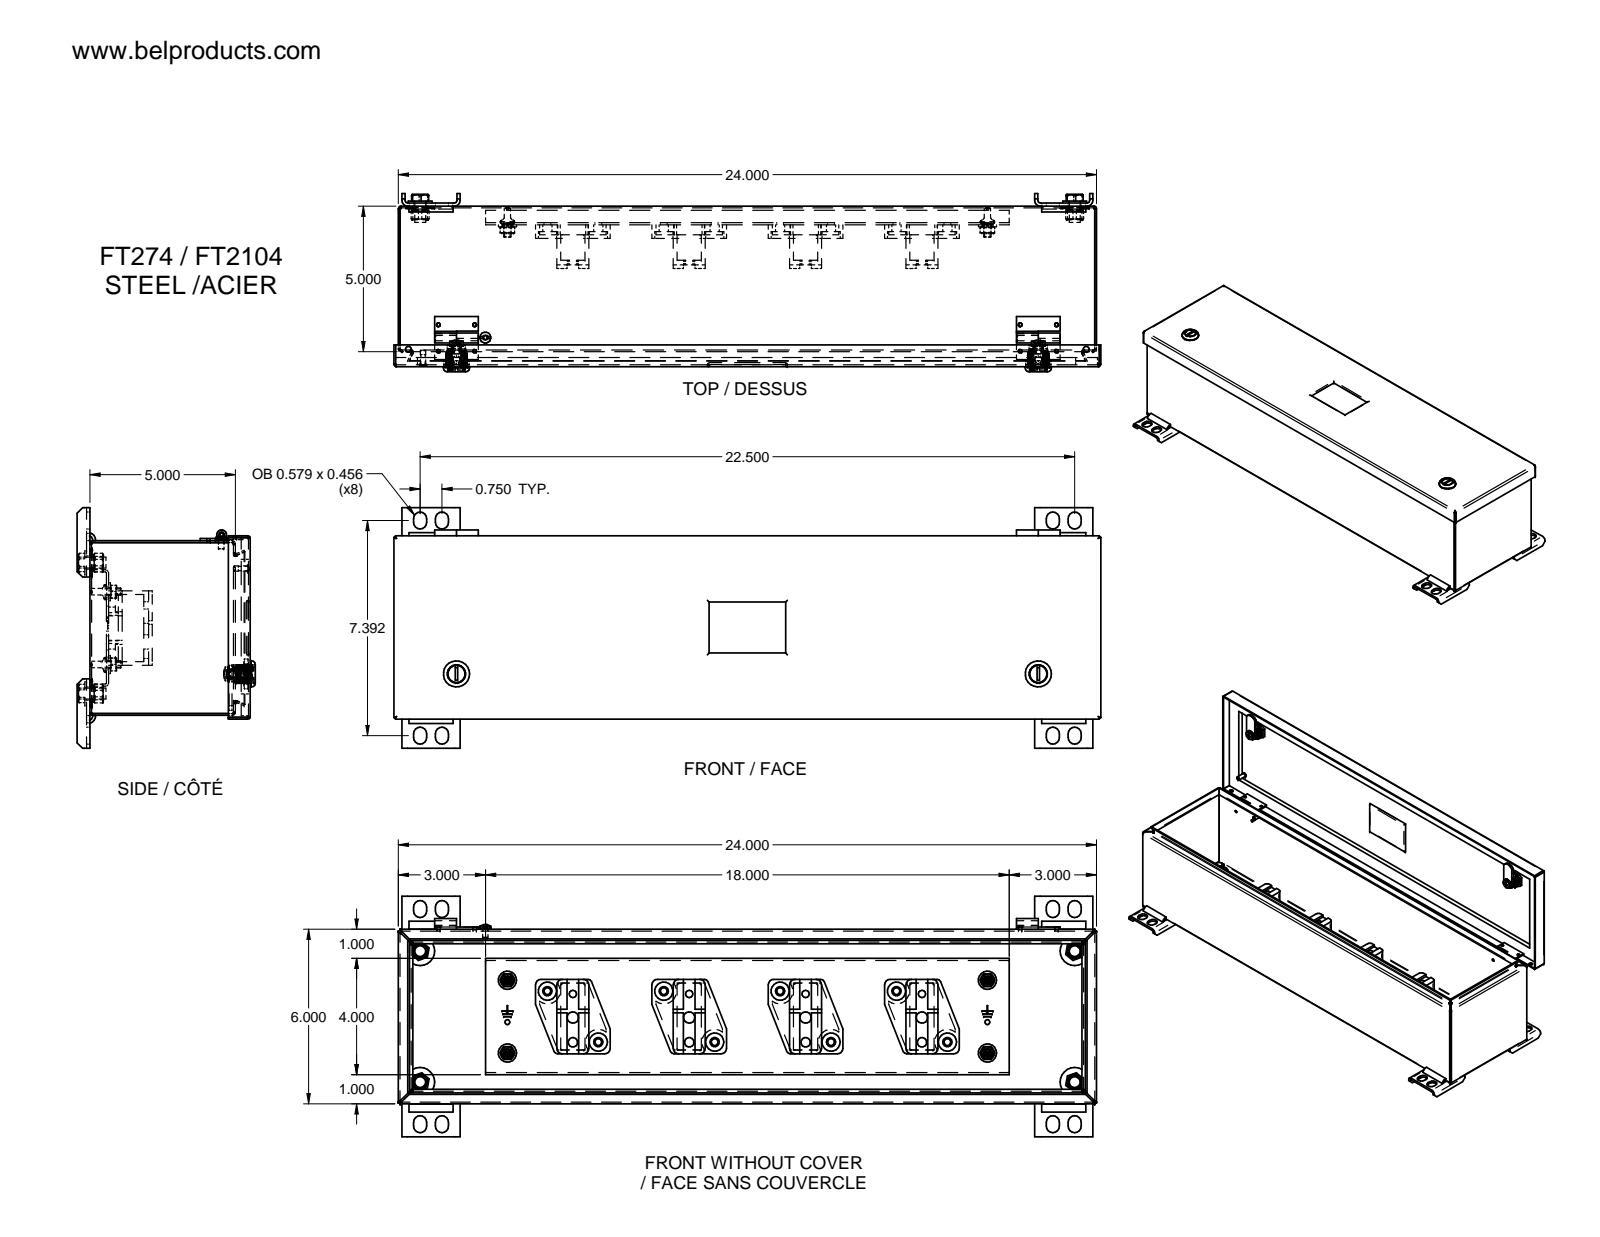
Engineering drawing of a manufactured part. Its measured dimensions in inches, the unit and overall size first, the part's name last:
Units: inches
Overall size (bounding box): 24.3 × 8.266 × 6.125
Round holes (diameter × count): ⌀0.124 ×8, ⌀0.13 ×8, ⌀0.236 ×8, ⌀0.25 ×8, ⌀0.312 ×8, ⌀0.375 ×8, ⌀0.456 ×8, ⌀0.625 ×8, ⌀0.125 ×5, ⌀0.281 ×4, ⌀0.324 ×4, ⌀0.355 ×4
Round bosses / shafts (diameter × count): ⌀0.125 ×8, ⌀0.119 ×5, ⌀0.812 ×4, ⌀0.625 ×4, ⌀0.219 ×4, ⌀0.031 ×4, ⌀0.9 ×2, ⌀0.89 ×2
Partial cylindrical surfaces — rounded edges, fillets, slot ends (radius × count): R0.187 ×28, R0.375 ×22, R0.032 ×18, R0.01 ×16, R0.057 ×16, R0.092 ×16, R0.228 ×16, R0.06 ×8
Main face-to-face distances: 0.06, 5.94, 0.06, 5.454, 5.514, 5.394, 5.454, 6, 5.88, 0.641
Hole centre spacings: 4, 8, 0.907, 2.475, 6.011, 20, 0.88, 1.215
Volume: 71.46 in³ · Surface area: 1 900 in²
Bodies: 69 solids, 2526 faces (1504 planar, 496 cylindrical, 526 other)
Part name (STEP PRODUCT): LOCK AVEC TOURNEVIS TYPE 4-12 SANS CAME-oa8; HOSING-oa0; INSERT POUR TOURNEVIS-oa1; NOIX DE FIXATION-oa2 (+8 more)
STEP written by: Unknown (AUTOMOTIVE_DESIGN)
